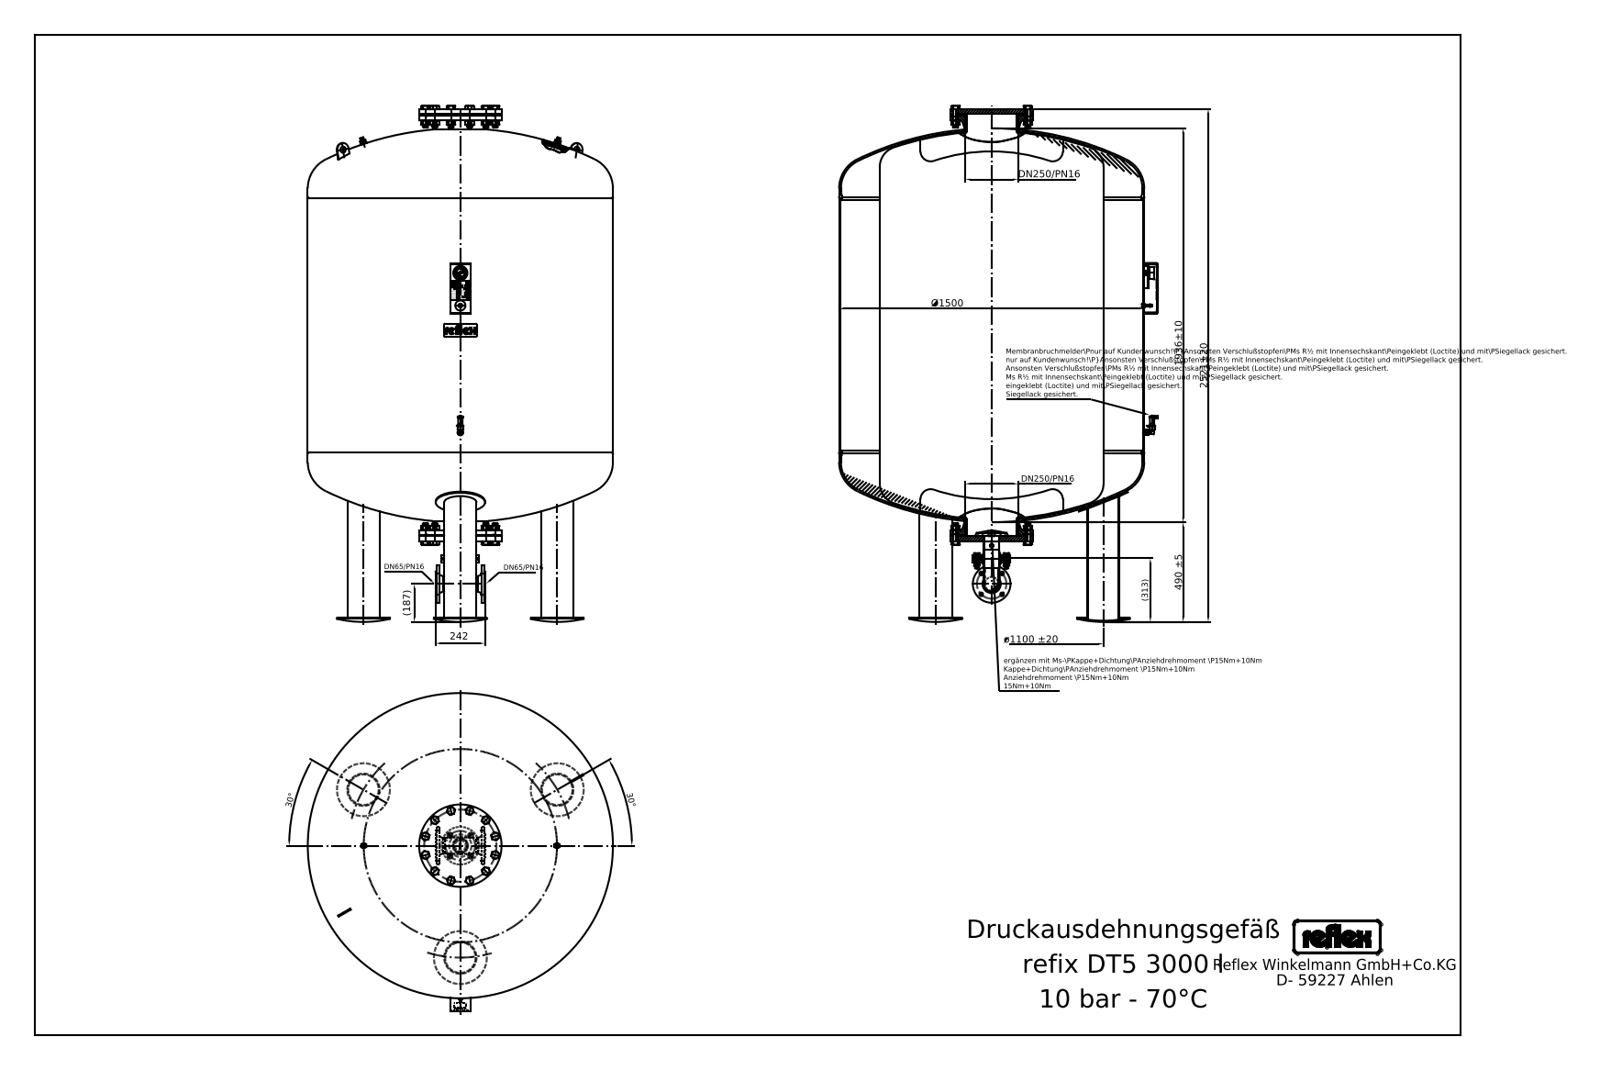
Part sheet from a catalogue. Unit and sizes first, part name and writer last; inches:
Units: inches
Overall size (bounding box): 99.606 × 61.654 × 59.055
Round holes (diameter × count): ⌀0.748 ×4, ⌀0.394 ×1, ⌀1.181 ×1, ⌀1.969 ×1, ⌀2.717 ×1, ⌀2.996 ×1, ⌀10.252 ×1
Round bosses / shafts (diameter × count): ⌀0.63 ×16, ⌀6.26 ×3, ⌀1.102 ×2, ⌀1.024 ×2, ⌀0.787 ×2, ⌀59.055 ×1, ⌀15.945 ×1, ⌀10.748 ×1
Partial cylindrical surfaces — rounded edges, fillets, slot ends (radius × count): R0.221 ×4, R0.089 ×3, R0.039 ×2, R0.151 ×2, R0.197 ×2, R0.266 ×2, R0.365 ×2, R0.37 ×2
Main face-to-face distances: 50.236, 1.024, 82.205, 1.22, 80.984, 2.244, 16.693, 66.929, 79.961, 15.276
Hole centre spacings: 2.855, 4.037, 5.709, 3.241, 30.138
Volume: 190 000 in³ · Surface area: 32 570 in²
Bodies: 28 solids, 982 faces (550 planar, 222 cylindrical, 210 other)
STEP written by: Mechanical Desktop 2008 (CONFIG_CONTROL_DESIGN)
